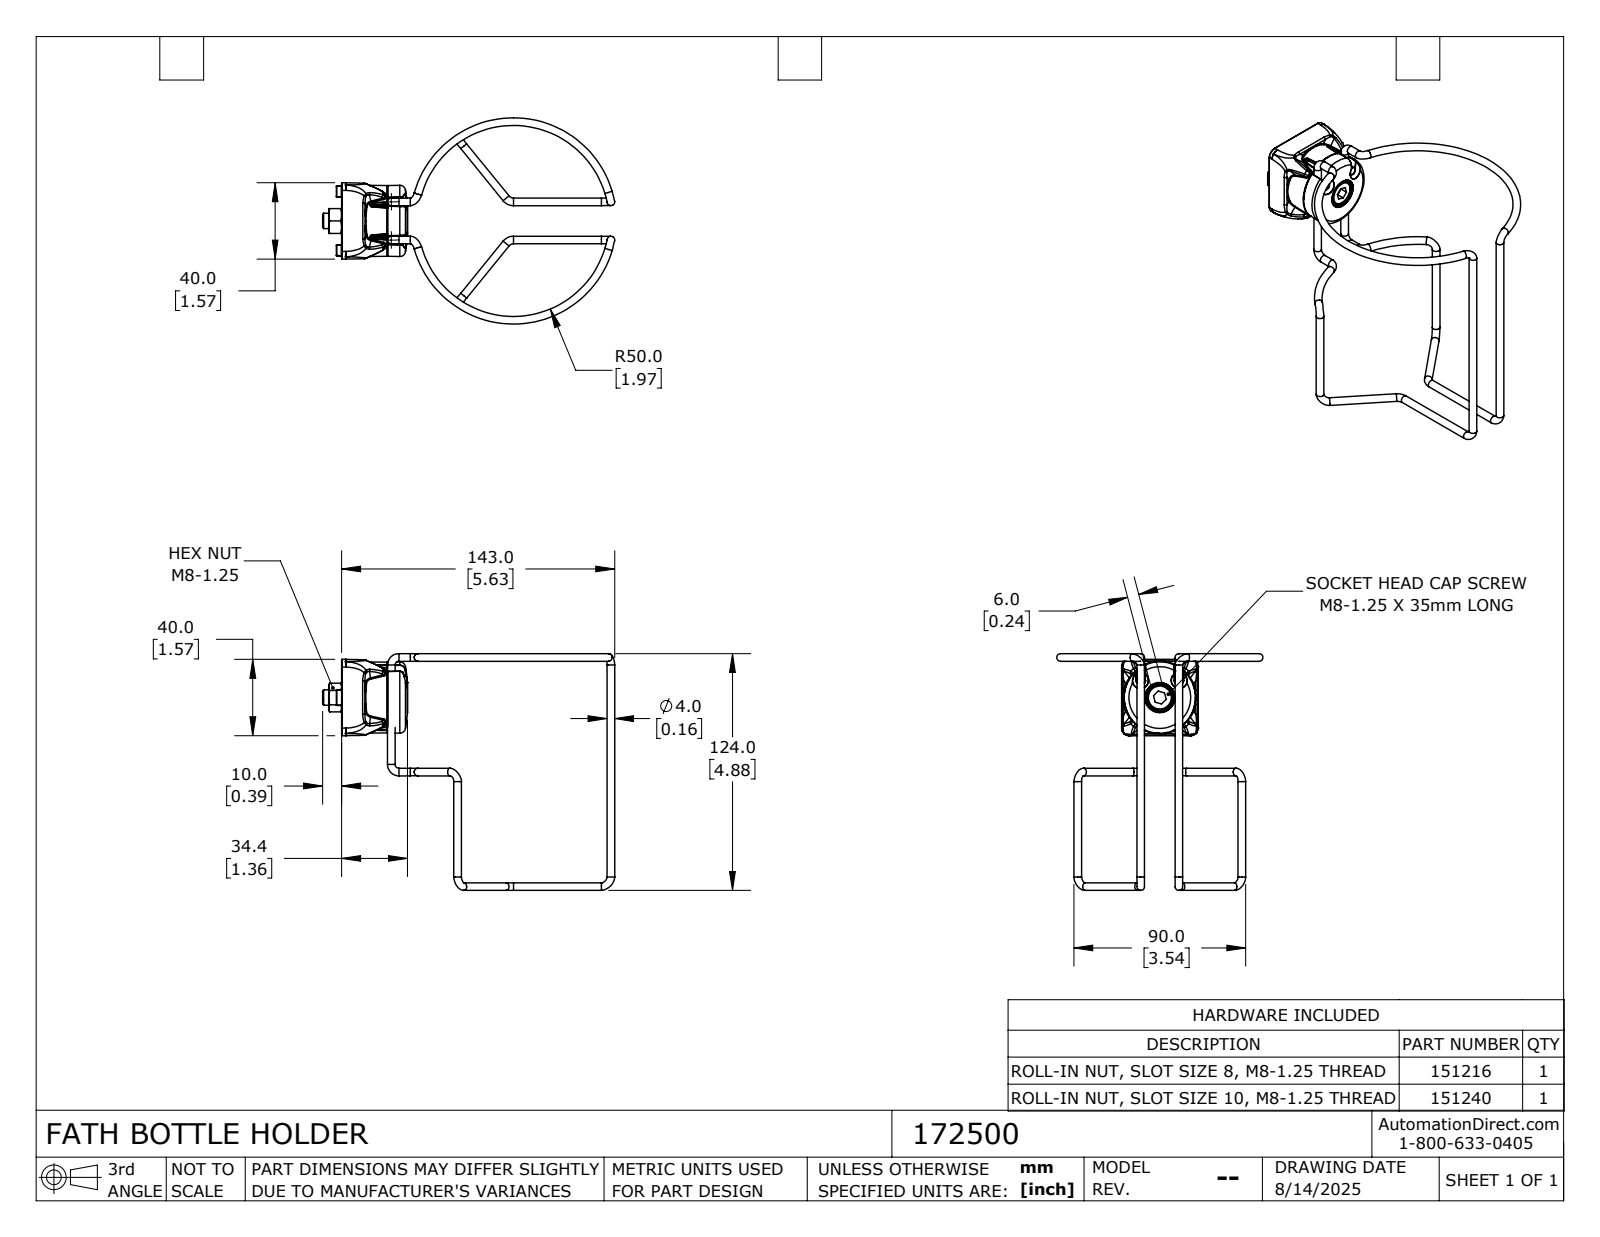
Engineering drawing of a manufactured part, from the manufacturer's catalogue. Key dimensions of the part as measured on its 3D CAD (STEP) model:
Part name (STEP PRODUCT): 172500
STEP written by: SolidWorks 2024 (CONFIG_CONTROL_DESIGN)
Units: millimetres
Bodies: 8 solids, 1307 faces (224 planar, 324 cylindrical, 759 other)
Overall size (bounding box): 153.03 × 124 × 108
Volume: 51 369 mm³ · Surface area: 32 666 mm²
Round holes (diameter × count): ⌀6.8 ×1, ⌀8 ×1, ⌀13.01 ×1
Round bosses / shafts (diameter × count): ⌀4 ×17, ⌀13 ×1
Partial cylindrical surfaces — rounded edges, fillets, slot ends (radius × count): R0.2 ×142, R0.5 ×22, R1 ×8, R4 ×8, R1.2 ×4, R2.15 ×2, R16.5 ×1
Main face-to-face distances: 13.5, 30.8, 8, 6, 13.3, 10.7, 17, 10.5, 24, 9.2
